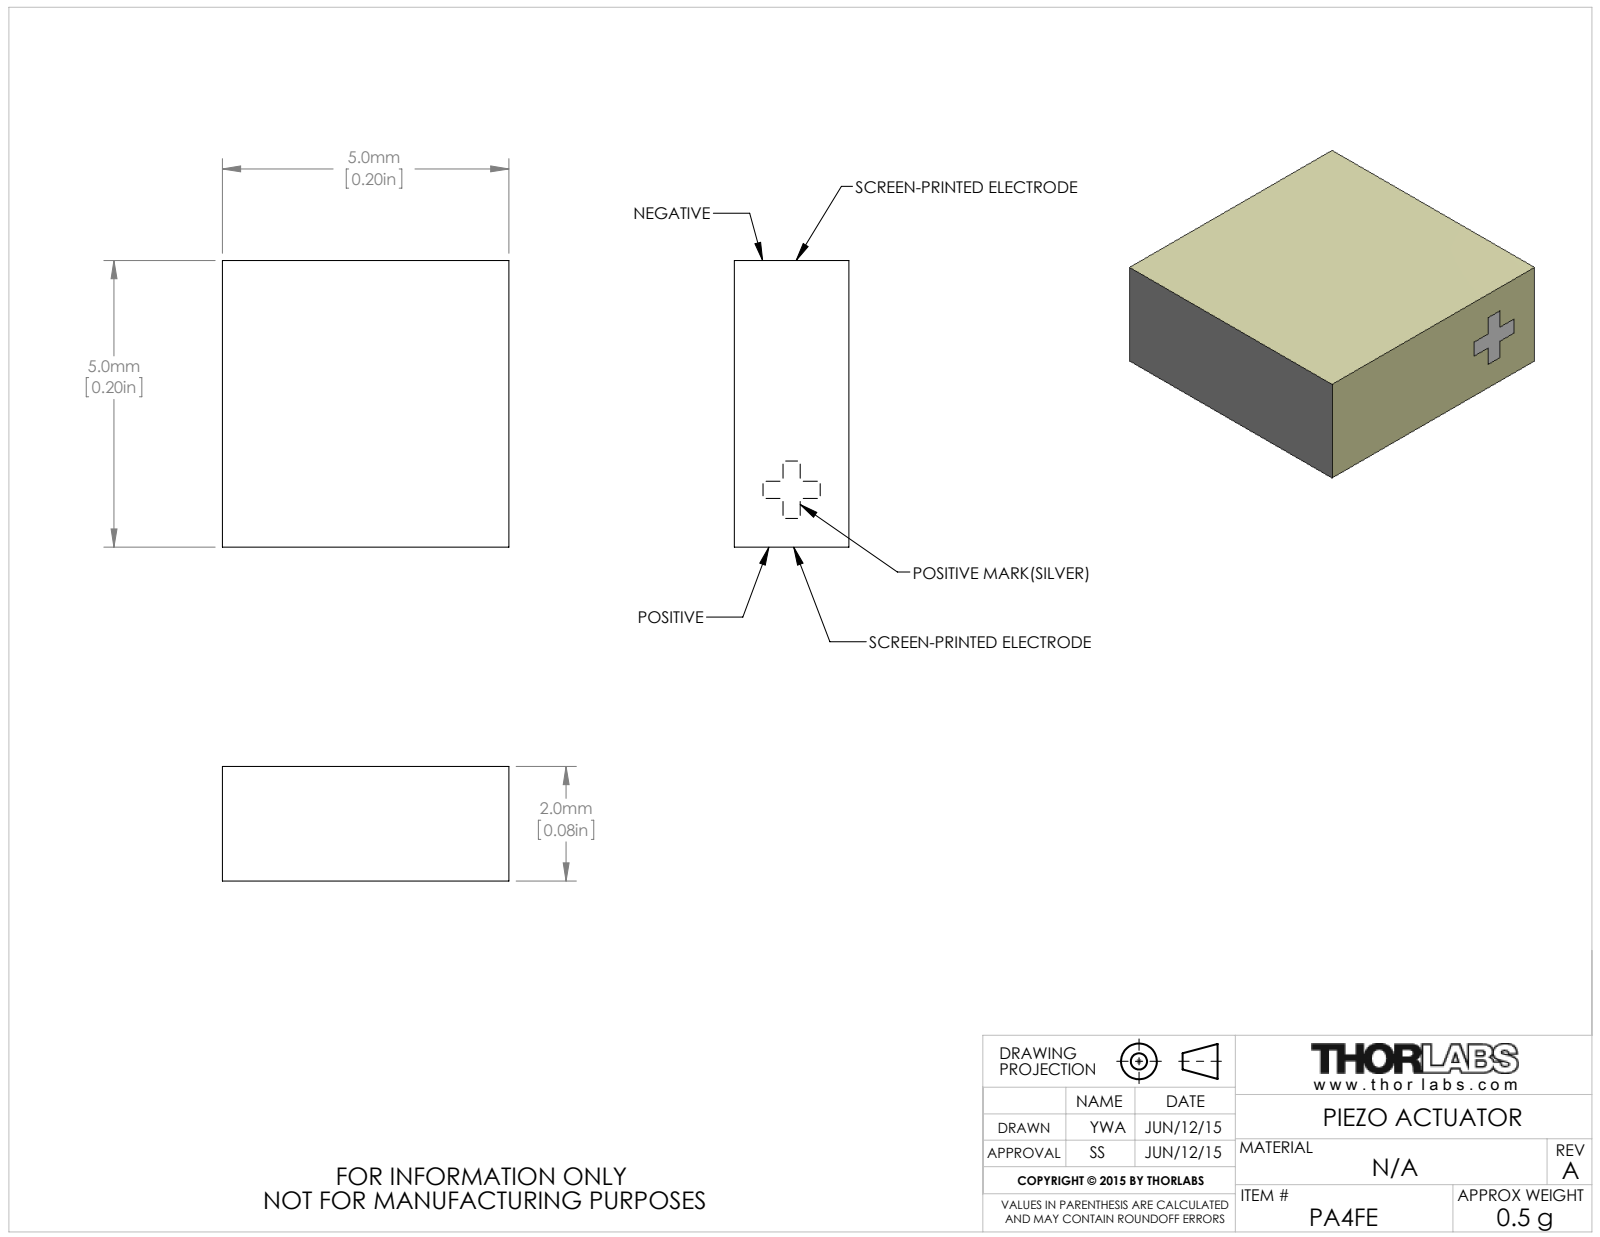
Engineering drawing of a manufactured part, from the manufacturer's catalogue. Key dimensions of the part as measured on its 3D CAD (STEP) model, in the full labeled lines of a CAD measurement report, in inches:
Part name (STEP PRODUCT): CTN002585
STEP written by: SolidWorks 2014 (AUTOMOTIVE_DESIGN)
Units: inches
Bodies: 1 solid, 7 faces (7 planar, 0 cylindrical, 0 other)
Overall size (bounding box): 0.197 × 0.197 × 0.079
Volume: 0.003 in³ · Surface area: 0.14 in²
Main face-to-face distances: 0.079, 0.197
